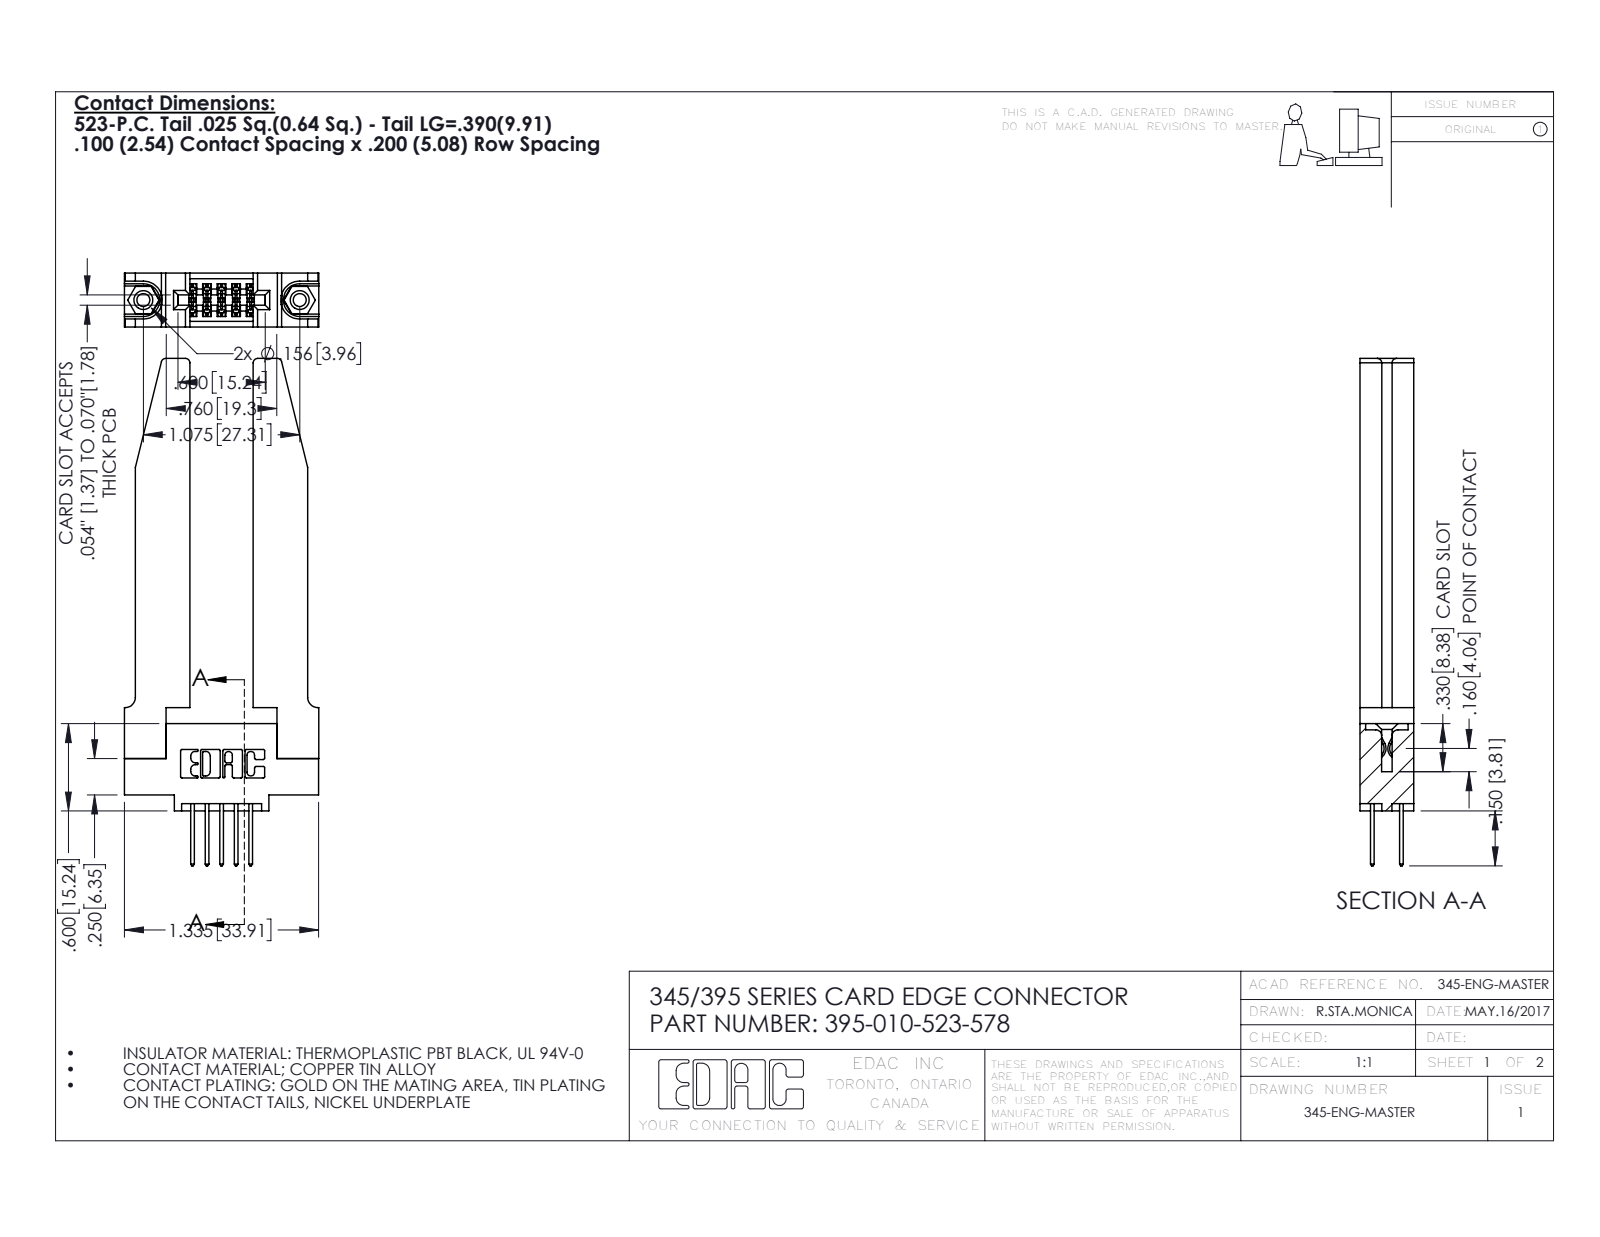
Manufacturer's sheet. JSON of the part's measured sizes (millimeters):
{"part_name": "395-010-523-578; 345-250-001_345-250-001-102; 345-292-001_345-293-123; 345-220-078_345-220-078 (+1 more)", "step_written_by": "SolidWorks 2016 (CONFIG_CONTROL_DESIGN)", "units": "millimeters", "bodies": {"solids": 15, "faces": 864, "planar": 556, "cylindrical": 256, "other": 52}, "overall_size": [88.6, 33.9, 9.4], "volume_mm3": 10700, "surface_area_mm2": 10590, "round_holes": [[2.3, 2], [3.2, 2], [4, 2], [1.6, 1]], "round_bosses_or_shafts": [[3.9, 2]], "partial_cylinders_radius": [[0.3, 22], [0.2, 15], [0.3, 10], [0.8, 8], [0.2, 6], [0.8, 6], [0.7, 3], [0.4, 2]], "face_to_face_distances": [9.4, 3.8, 5.6, 11, 1.8, 3.8, 7.6, 2, 5.1, 1.8], "hole_center_spacings": [6.9, 21.5, 27.3]}
